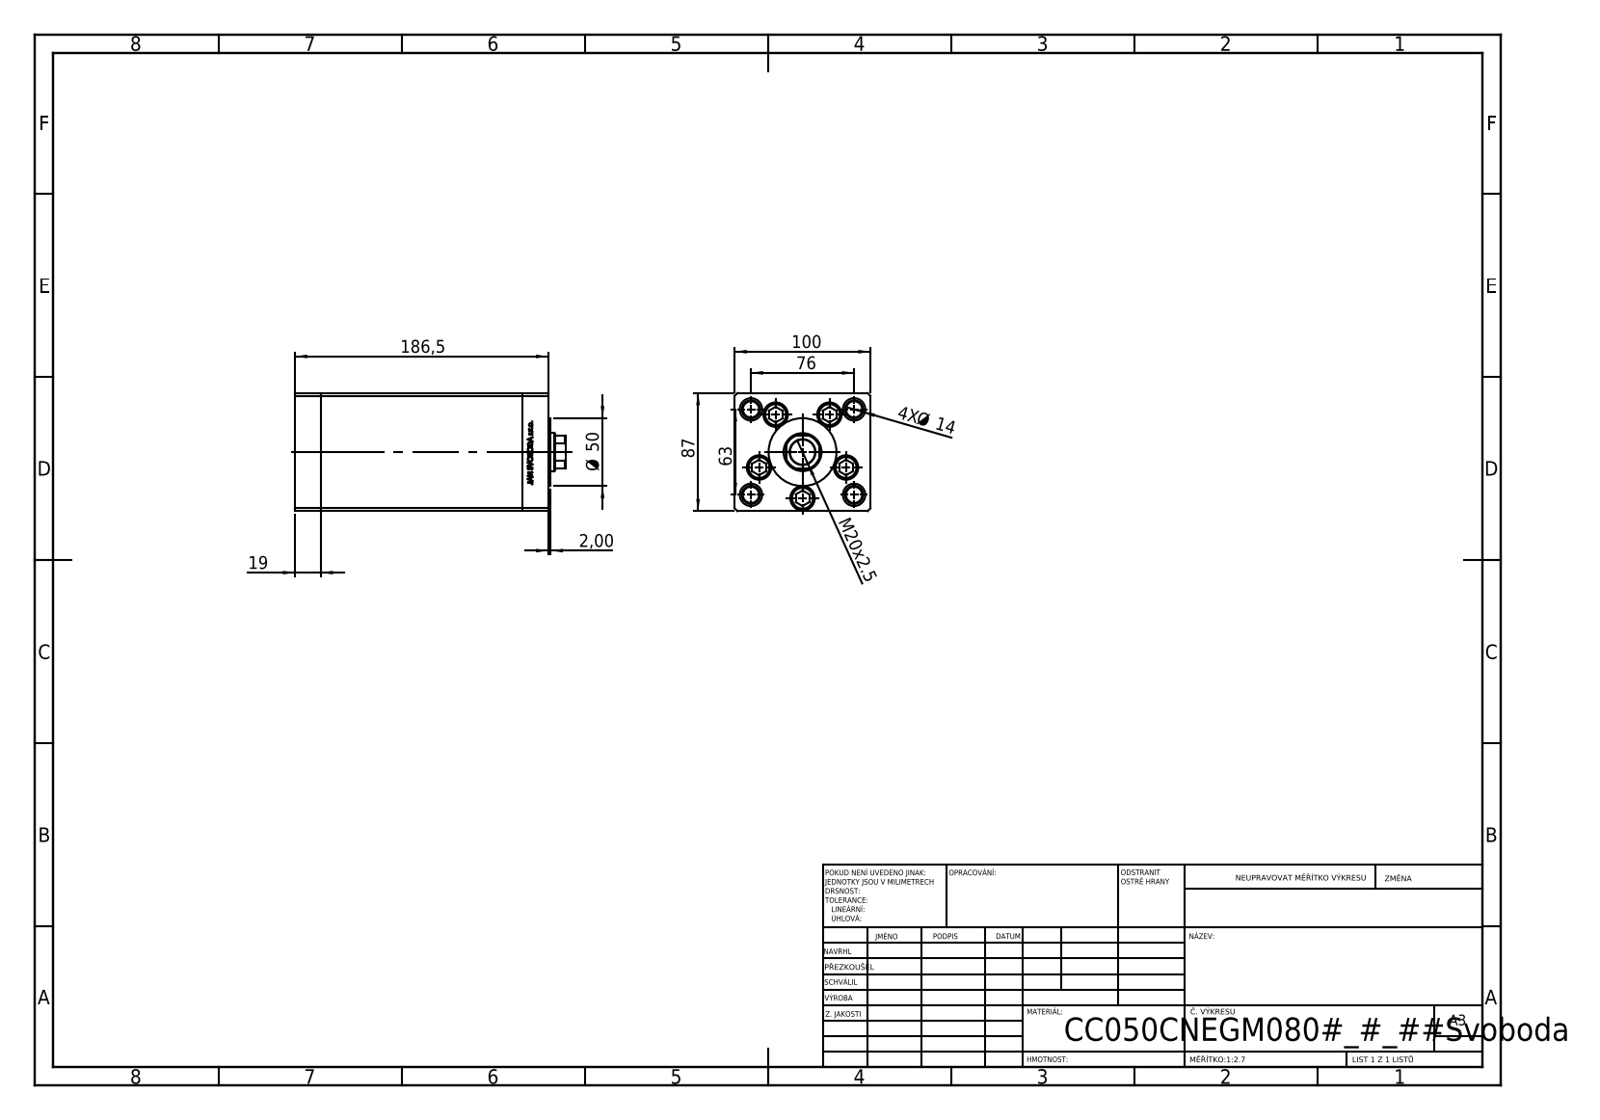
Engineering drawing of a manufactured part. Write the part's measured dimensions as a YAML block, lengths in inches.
part_name: "V220C FRONT; V220C BACK_C; ALLEN BOLT; V220C_VC_C (+1 more)"
step_written_by: "SolidWorks 2019 (CONFIG_CONTROL_DESIGN)"
units: inches
bodies: {solids: 13, faces: 1160, planar: 538, cylindrical: 160, other: 462}
overall_size: [7.854, 3.937, 3.425]
volume: 81.47
surface_area: 354.3
round_holes:
  - {diameter: 0.531, count: 9}
  - {diameter: 0.709, count: 5}
  - {diameter: 0.472, count: 4}
  - {diameter: 0.65, count: 4}
  - {diameter: 0.669, count: 1}
  - {diameter: 0.728, count: 1}
  - {diameter: 1.102, count: 1}
round_bosses_or_shafts:
  - {diameter: 0.315, count: 5}
  - {diameter: 0.669, count: 4}
  - {diameter: 1.969, count: 1}
partial_cylinders:
  - {radius: 0.037, count: 2}
  - {radius: 0.531, count: 1}
face_to_face_distances: [3.937, 3.425, 0.748, 5.846, 6.594, 1.348, 7.343, 5.994, 5.246, 0.6]
hole_center_spacings: [1.339, 1.943, 0.732, 0.828, 1.499, 1.546, 1.607, 1.702]
